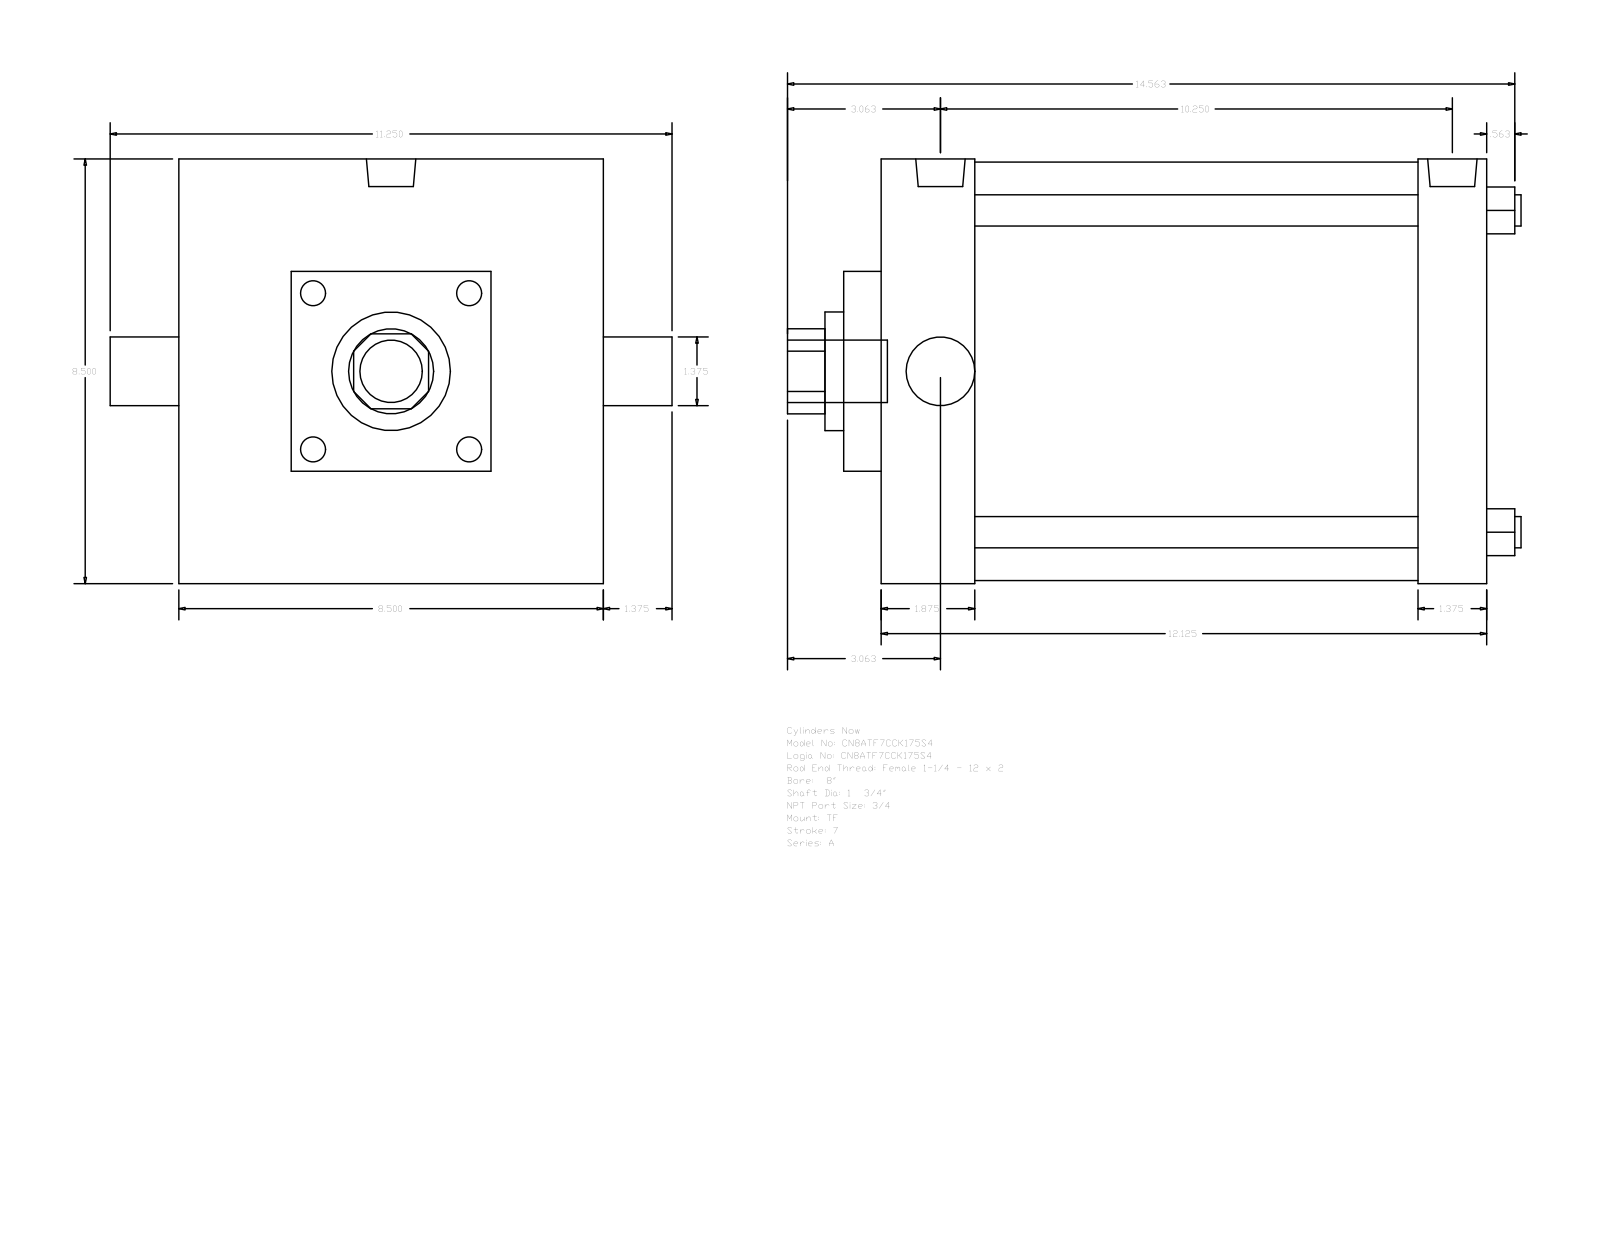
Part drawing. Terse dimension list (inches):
name: A_TF__0800_1.75
written by: GSSL Pune (CONFIG_CONTROL_DESIGN)
unit: in
bodies: 0 solids, 89 faces (65 planar, 24 cylindrical, 0 other)
size: 14.687 × 11.25 × 8.5
holes: 4× ⌀0.625, 1× ⌀1.375, 1× ⌀1.75, 1× ⌀2.375, 1× ⌀8.375
bosses: 3× ⌀0.594, 2× ⌀0.989, 1× ⌀1.25
rounds: 1× R0.852
face distances: 12.125, 8.5, 1.375, 1.875, 10.25, 10.75, 8.875, 0.75, 2.25, 6.25
hole spacings: 4.554, 6.44, 9.108
